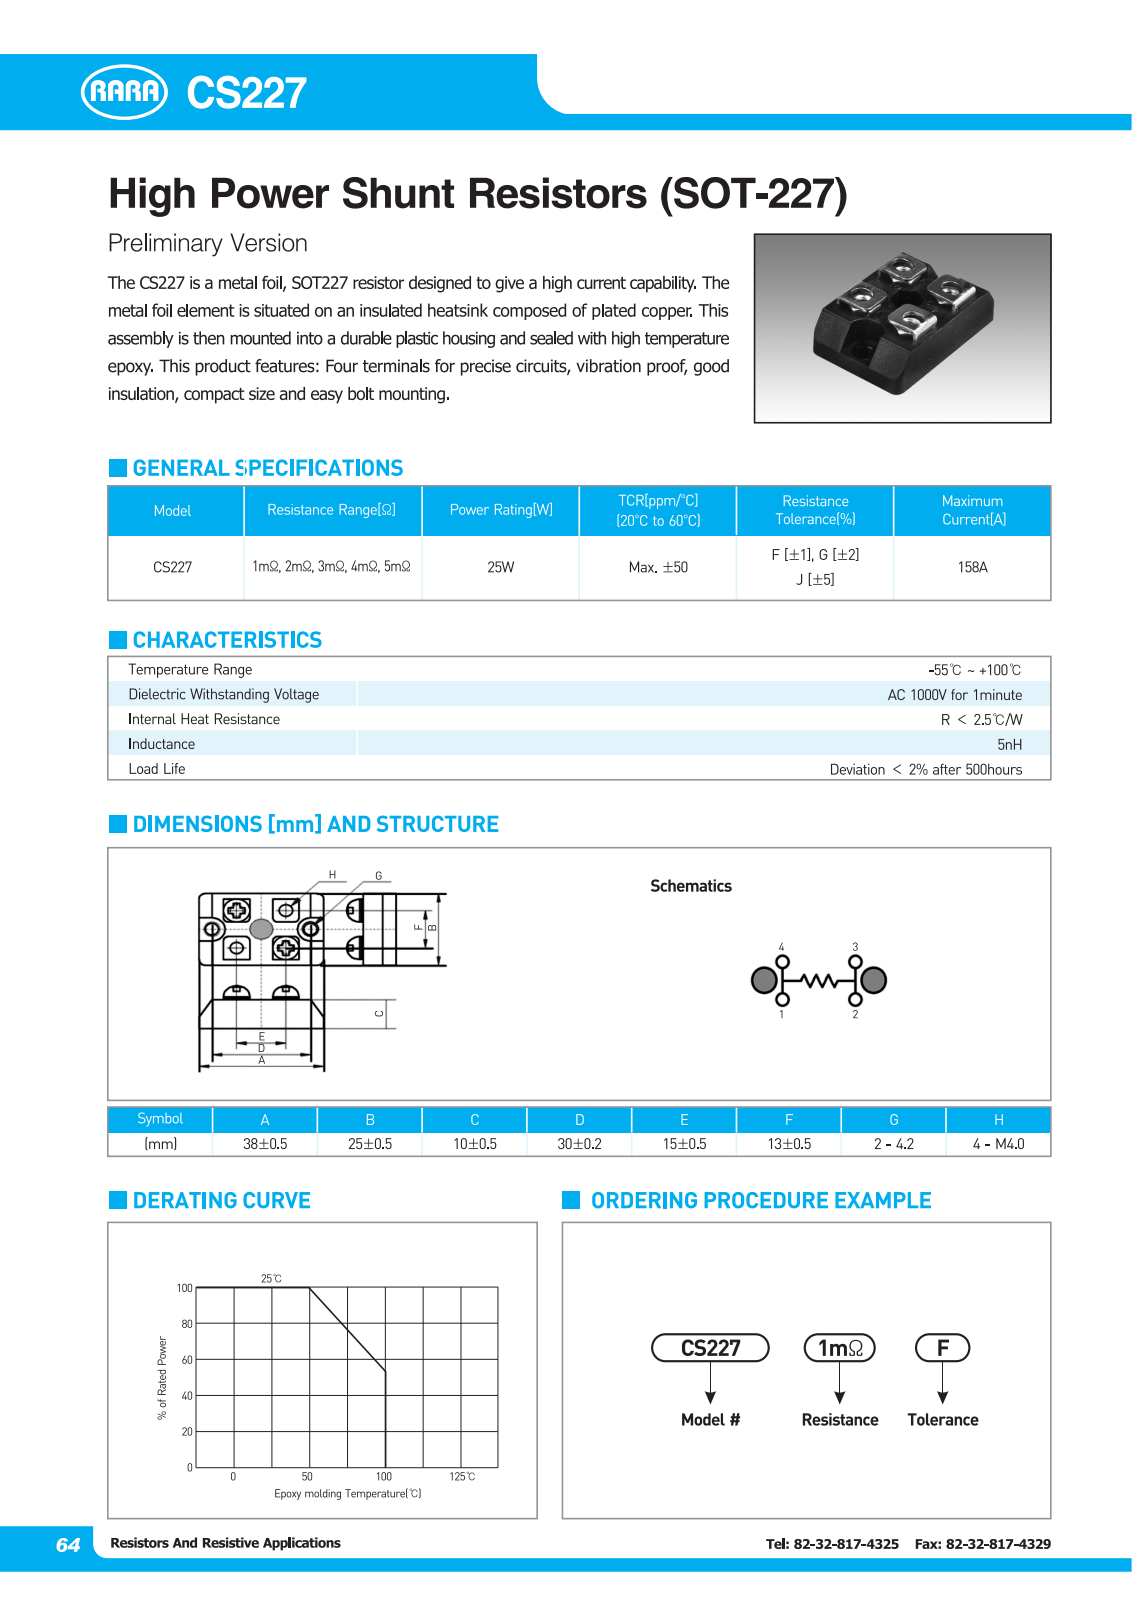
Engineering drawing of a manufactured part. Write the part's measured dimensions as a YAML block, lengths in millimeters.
part_name: "091-004; Ecrou HM4 (CE); 211045; 240101_Plaquette à plat (+5 more)"
step_written_by: "ST-DEVELOPER v16.7 (AUTOMOTIVE_DESIGN)"
units: millimeters
bodies: {solids: 25, faces: 1094, planar: 498, cylindrical: 307, other: 289}
overall_size: [38.2, 25, 12.1]
volume: 6898
surface_area: 5924
round_holes:
  - {diameter: 3.3, count: 4}
  - {diameter: 4.8, count: 2}
  - {diameter: 3, count: 1}
partial_cylinders:
  - {radius: 0.2, count: 62}
  - {radius: 2.25, count: 34}
  - {radius: 0.1, count: 29}
  - {radius: 0.3, count: 28}
  - {radius: 0.33, count: 26}
  - {radius: 0.5, count: 20}
  - {radius: 1, count: 16}
  - {radius: 1.3, count: 4}
face_to_face_distances: [3.05, 2.9, 1, 6.35, 4.15, 3.15, 10.5, 7.35, 7.2, 7.05]
hole_center_spacings: [9.83, 23.38, 6.35, 12.7, 15, 16.29, 19.65, 7.5]
